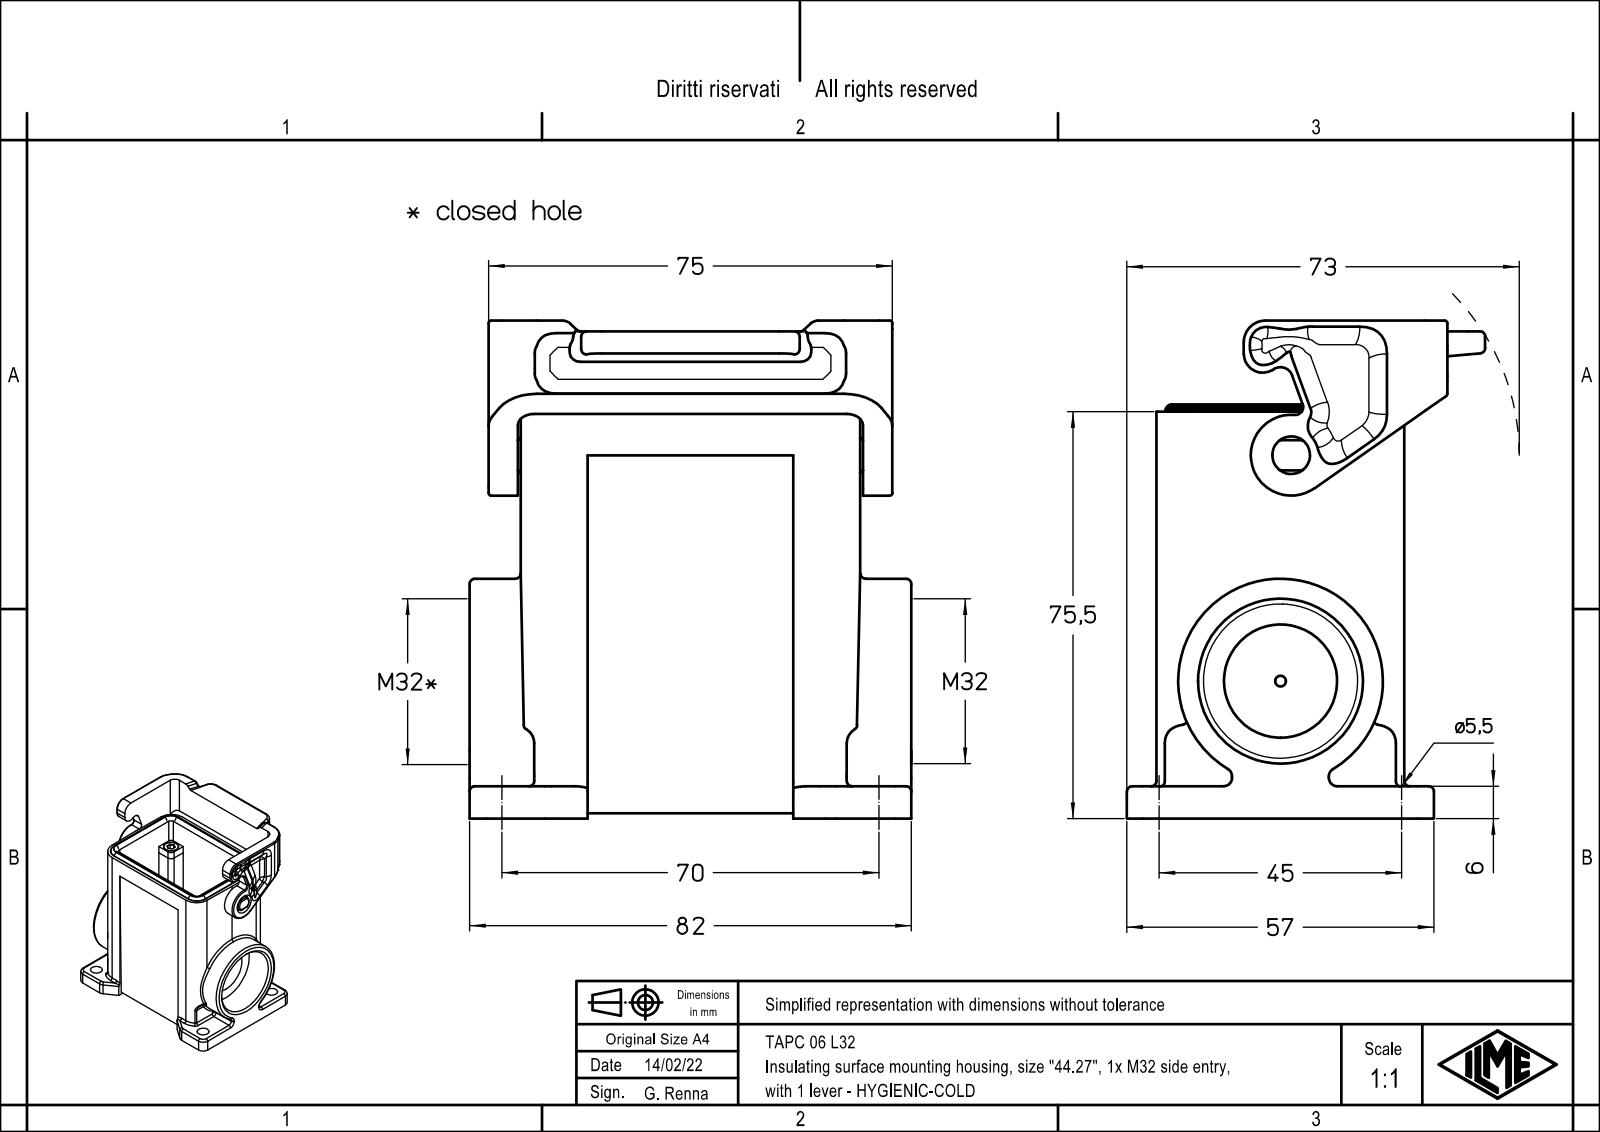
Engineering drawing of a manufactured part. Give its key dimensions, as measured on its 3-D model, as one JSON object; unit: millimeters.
{"part_name": "TAPH 06 L32", "step_written_by": "Creo Elements/Direct Modeling 20.1B 02-Apr-2019 (C) Parametric Technology GmbH (AUTOMOTIVE_DESIGN)", "units": "millimeters", "bodies": {"solids": 1, "faces": 326, "planar": 162, "cylindrical": 128, "other": 36}, "overall_size": [92.4, 82, 66.5], "volume_mm3": 125546, "surface_area_mm2": 47943, "round_holes": [[5.5, 4], [28, 1], [30.6, 1]], "round_bosses_or_shafts": [[38, 1]], "partial_cylinders_radius": [[3, 17], [2, 10], [1.5, 9], [1, 8], [1.3, 8], [0.5, 4], [6, 4], [7, 4]], "face_to_face_distances": [46, 5.4, 40.6, 40.59, 35.19, 5.41, 5.5, 1, 14.9, 9], "hole_center_spacings": [45, 70, 83.22]}
